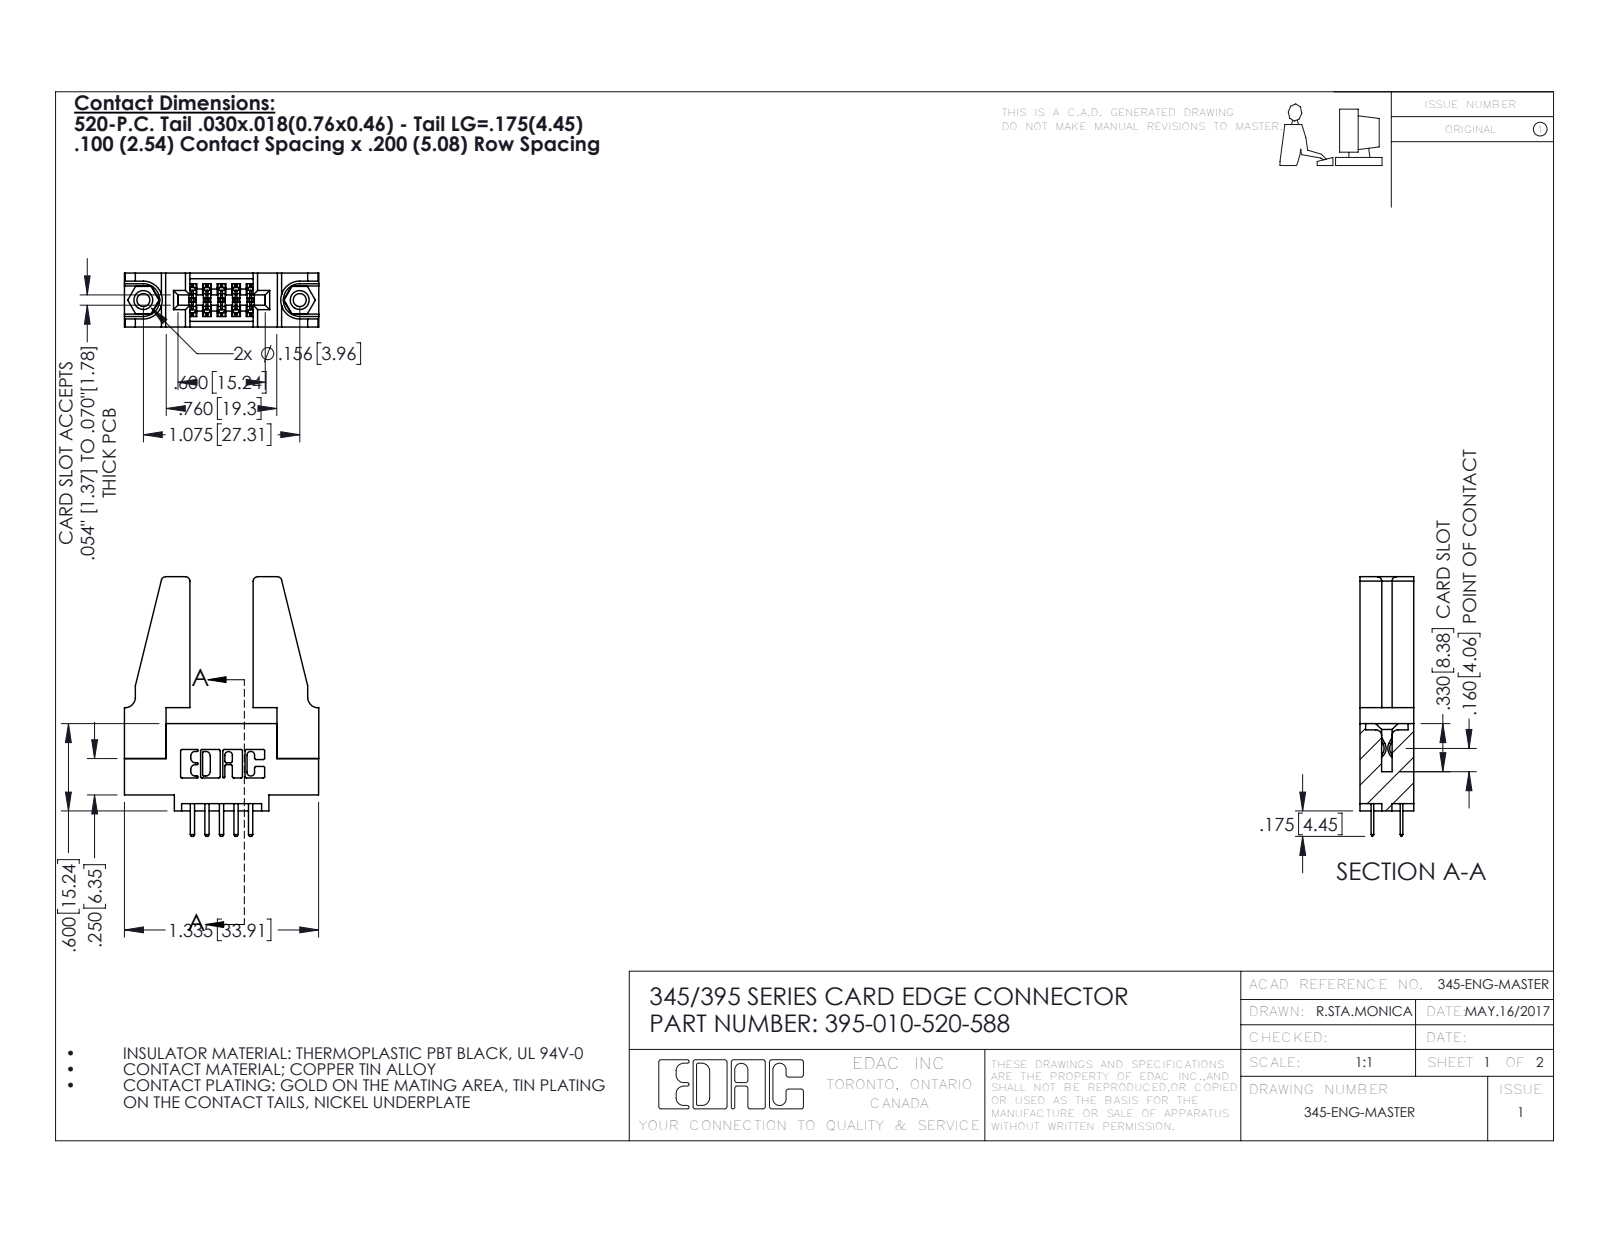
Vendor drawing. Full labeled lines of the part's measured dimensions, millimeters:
Part name (STEP PRODUCT): 345-250-001_345-250-001-102; 395-010-520-588; 345-292-001_345-293-120; 345-220-078_345-220-088 (+1 more)
STEP written by: SolidWorks 2016 (CONFIG_CONTROL_DESIGN)
Units: millimetres
Bodies: 15 solids, 794 faces (506 planar, 272 cylindrical, 16 other)
Overall size (bounding box): 45.3 × 33.9 × 9.4
Volume: 6 130 mm³ · Surface area: 6 742 mm²
Round holes (diameter × count): ⌀2.3 ×2, ⌀3.2 ×2, ⌀4 ×2, ⌀1.6 ×1
Round bosses / shafts (diameter × count): ⌀3.9 ×2
Partial cylindrical surfaces — rounded edges, fillets, slot ends (radius × count): R0.3 ×22, R0.2 ×15, R0.3 ×14, R0.8 ×8, R0.2 ×6, R0.8 ×6, R0.7 ×3, R0.4 ×2
Main face-to-face distances: 9.4, 1.8, 7.6, 5.1, 3.8, 5.6, 2, 3.8, 11.4, 7.3
Hole centre spacings: 6.9, 21.5, 27.3
